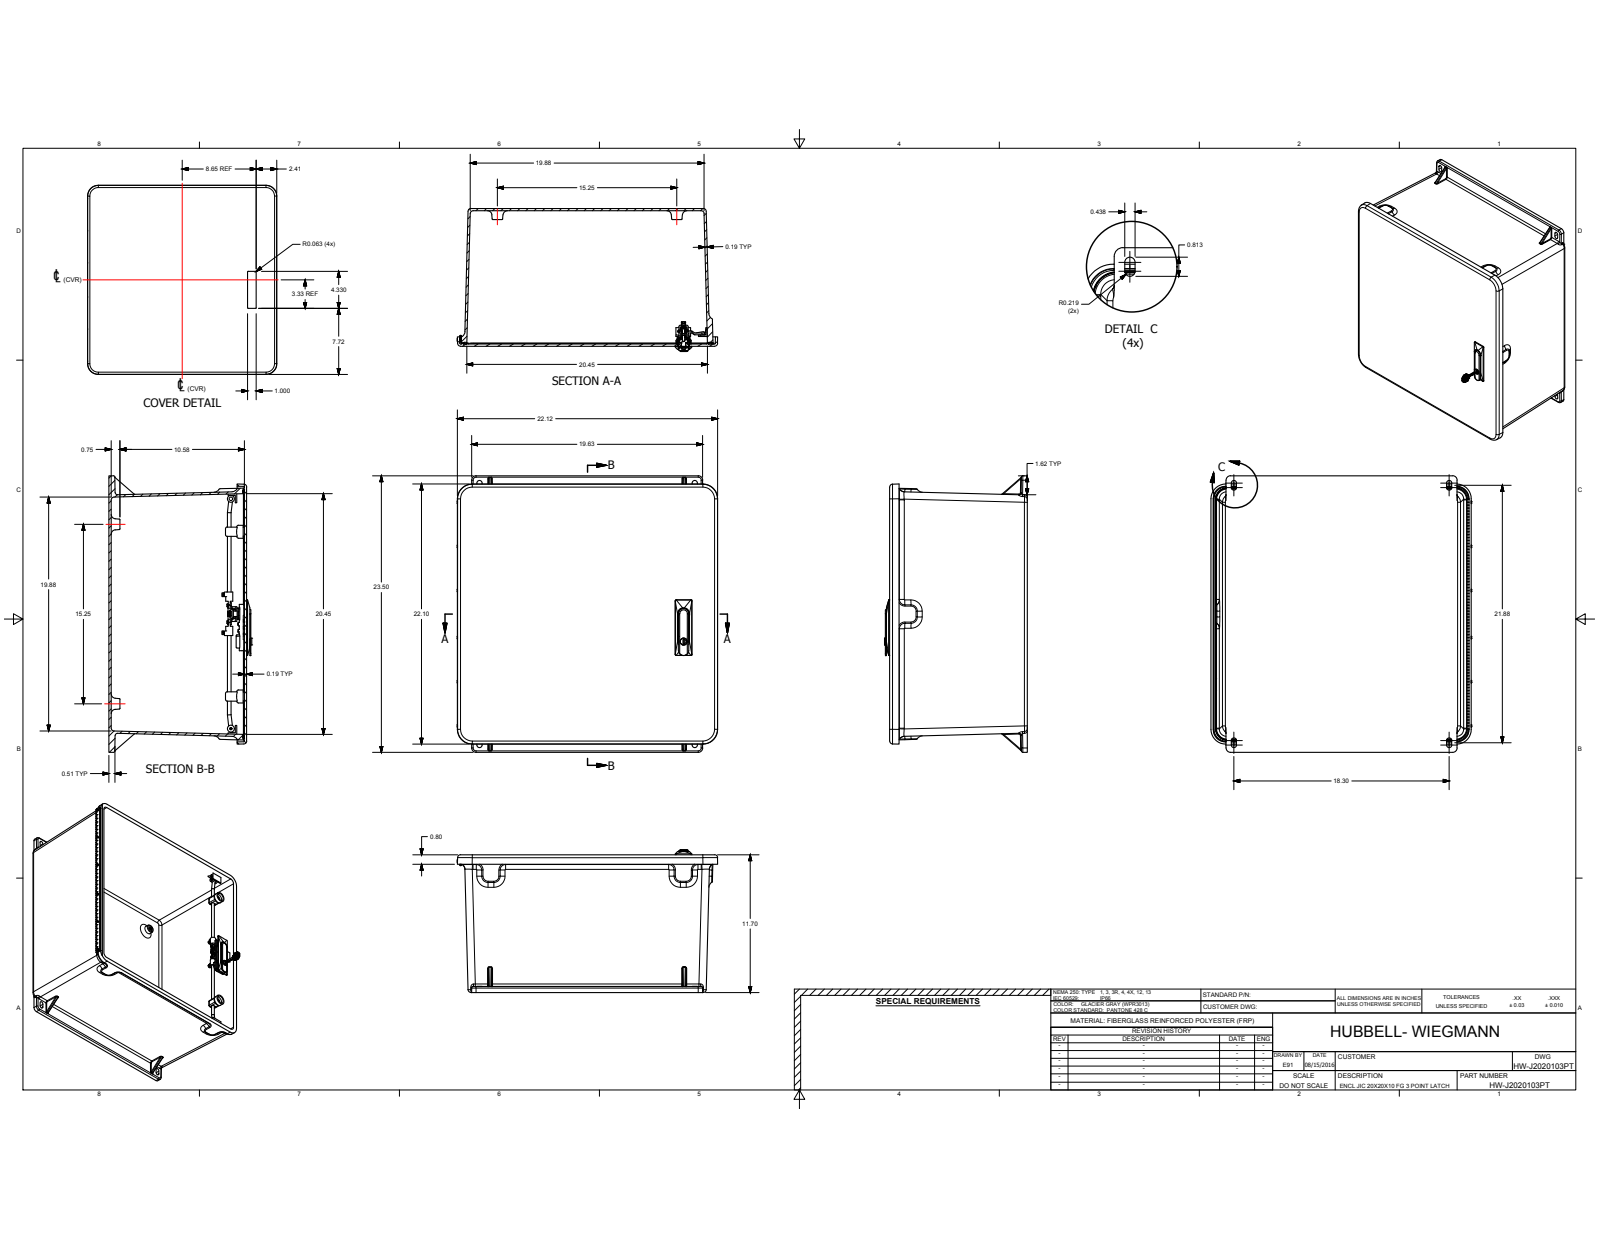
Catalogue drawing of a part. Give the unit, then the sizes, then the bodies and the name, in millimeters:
Units: millimetres
Overall size (bounding box): 596.9 × 562.33 × 364.65
Round holes (diameter × count): ⌀2.64 ×12, ⌀3.33 ×12, ⌀3.53 ×12, ⌀1.9 ×4, ⌀3.56 ×4, ⌀4.2 ×4, ⌀5 ×4, ⌀5.18 ×4, ⌀9.93 ×4, ⌀3 ×3, ⌀6.2 ×3, ⌀2.7 ×2
Round bosses / shafts (diameter × count): ⌀3.17 ×16, ⌀8.18 ×4, ⌀15 ×3, ⌀8 ×3, ⌀7.5 ×3, ⌀6 ×3, ⌀4 ×3, ⌀28 ×2
Partial cylindrical surfaces — rounded edges, fillets, slot ends (radius × count): R0.5 ×155, R0.13 ×72, R0.3 ×43, R0.51 ×36, R1 ×36, R1.59 ×28, R3.17 ×24, R2 ×21
Main face-to-face distances: 4.77, 292.43, 4.78, 297.2, 287.66, 12.04, 540.05, 7.26, 290.52, 285.75
Hole centre spacings: 95.25, 190.5, 6.35, 285.75, 387.35, 88.9, 101.6, 184.15
Volume: 6 816 000 mm³ · Surface area: 2 702 000 mm²
Bodies: 79 solids, 5186 faces (1681 planar, 2736 cylindrical, 769 other)
Part name (STEP PRODUCT): HW-J2020103PT; WP2020HBOX; RMINS25020A12-18; RMHING19-1-2 (+8 more)
STEP written by: Autodesk Inventor 2017 (CONFIG_CONTROL_DESIGN)
